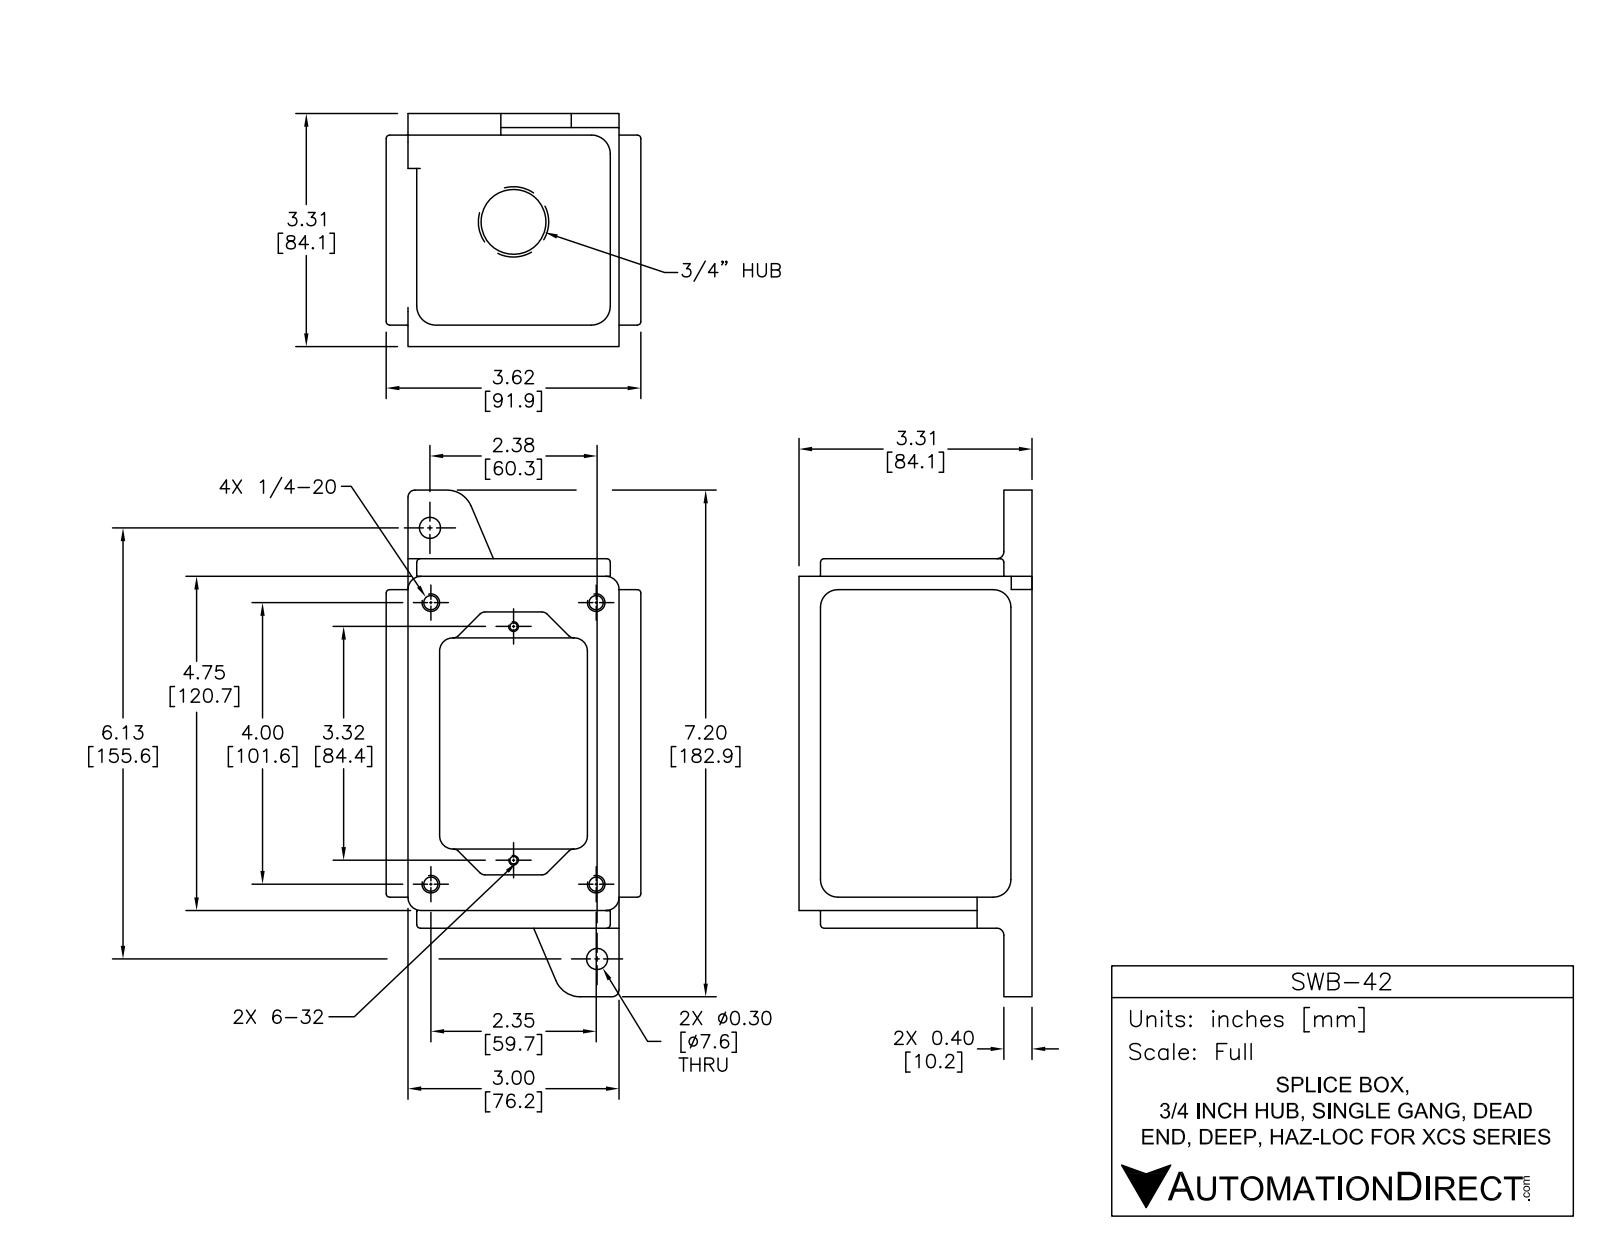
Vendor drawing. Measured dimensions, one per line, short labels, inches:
name: SWB-42
written by: SolidWorks 2015 (AUTOMOTIVE_DESIGN)
unit: in
bodies: 1 solid, 351 faces (154 planar, 113 cylindrical, 84 other)
size: 7.2 × 3.62 × 3.313
volume: 26.54 in³; area: 150.9 in²
holes: 4× ⌀0.201, 2× ⌀0.107, 2× ⌀0.29, 1× ⌀0.922
bosses: 1× ⌀0.3
rounds: 16× R0.05, 12× R0.01, 12× R0.1, 10× R0.375, 7× R0.188, 4× R0.02, 4× R0.21, 4× R0.25
face distances: 0.56, 3.06, 0.25, 3.62, 2.5, 0.2, 3.063, 3.313, 4.75, 0.05
hole spacings: 3.844, 1.223, 1.063, 1.838, 2.59, 4, 4.869, 5.063
